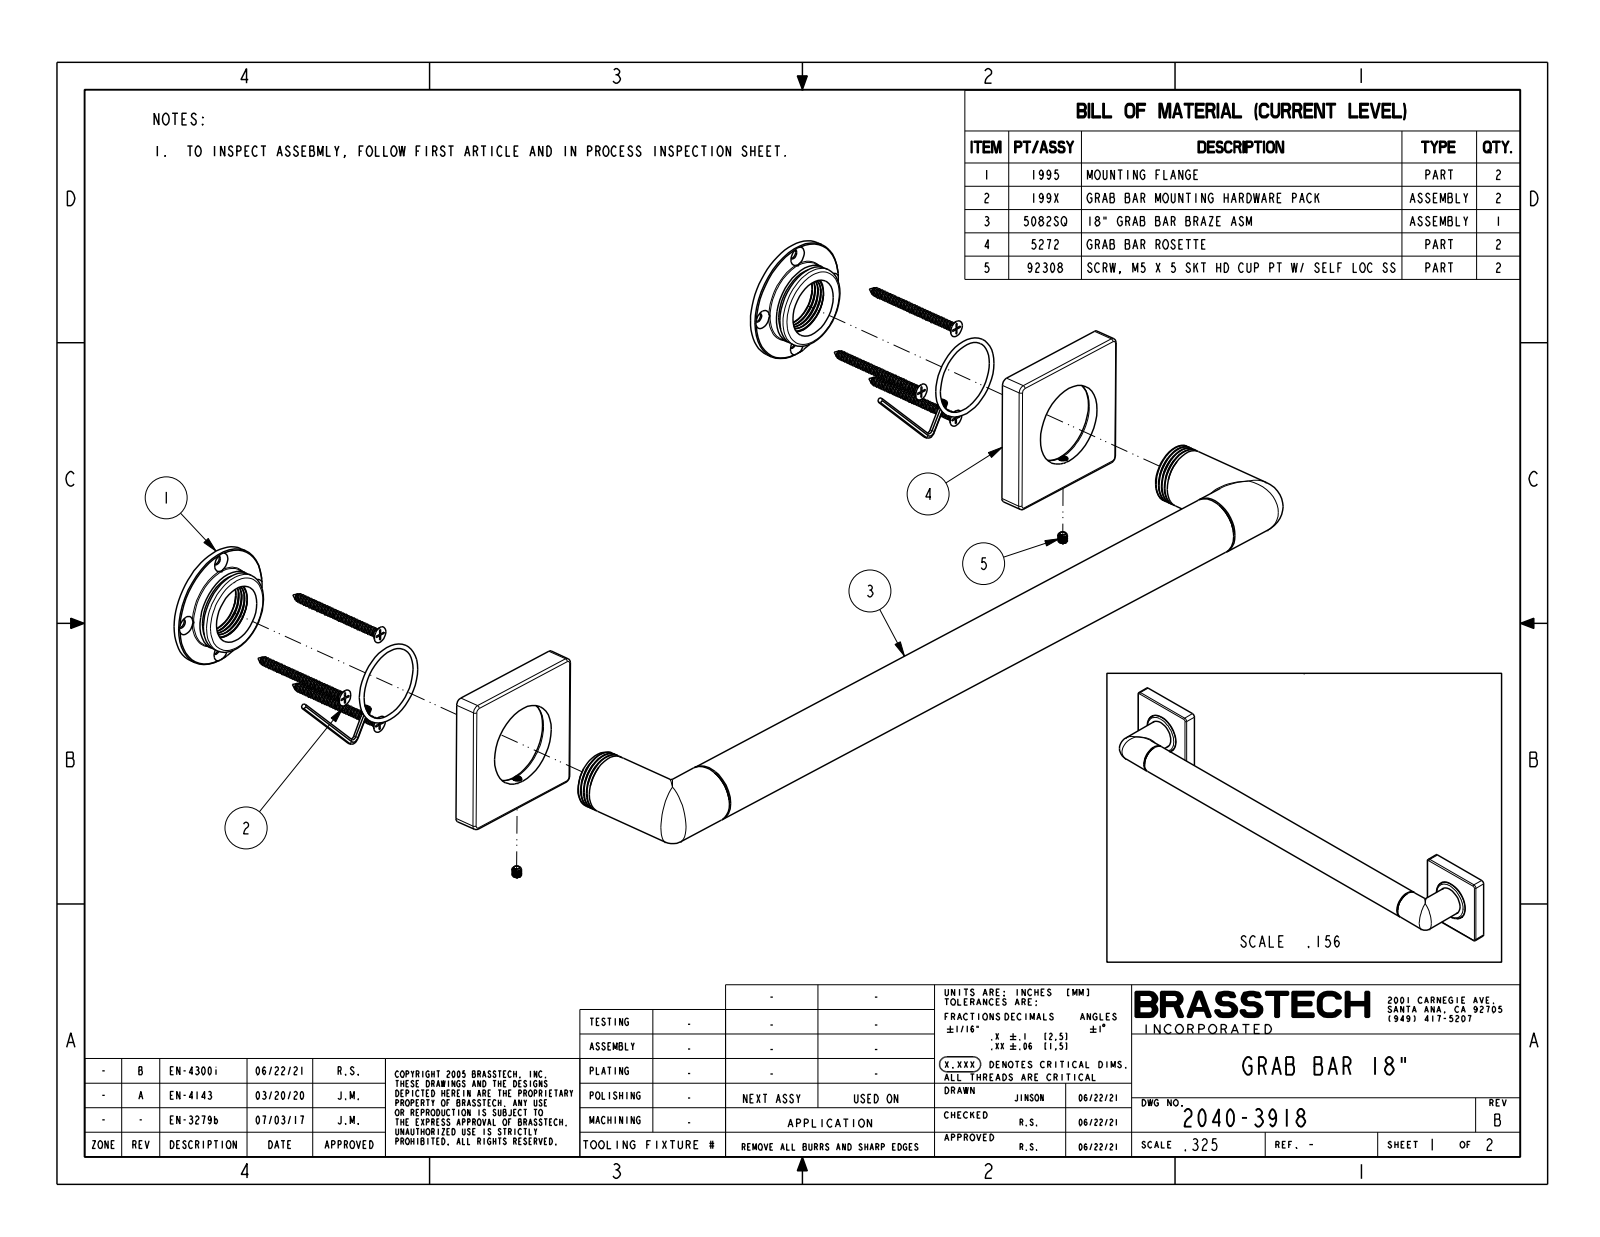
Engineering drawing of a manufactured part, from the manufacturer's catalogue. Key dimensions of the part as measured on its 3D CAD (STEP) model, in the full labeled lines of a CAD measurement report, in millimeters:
Part name (STEP PRODUCT): 2040-3918
STEP written by: CREO PARAMETRIC BY PTC INC, 2018400 (CONFIG_CONTROL_DESIGN)
Units: millimetres
Bodies: 1 solid, 72 faces (14 planar, 30 cylindrical, 28 other)
Overall size (bounding box): 533.4 × 76.2 × 70
Volume: 584 000 mm³ · Surface area: 82 840 mm²
Round bosses / shafts (diameter × count): ⌀31.8 ×3, ⌀44.5 ×2
Partial cylindrical surfaces — rounded edges, fillets, slot ends (radius × count): R3.2 ×8, R1.3 ×6
Main face-to-face distances: 13.5, 76.2, 457.2, 15.2, 1.8, 533.4, 381
